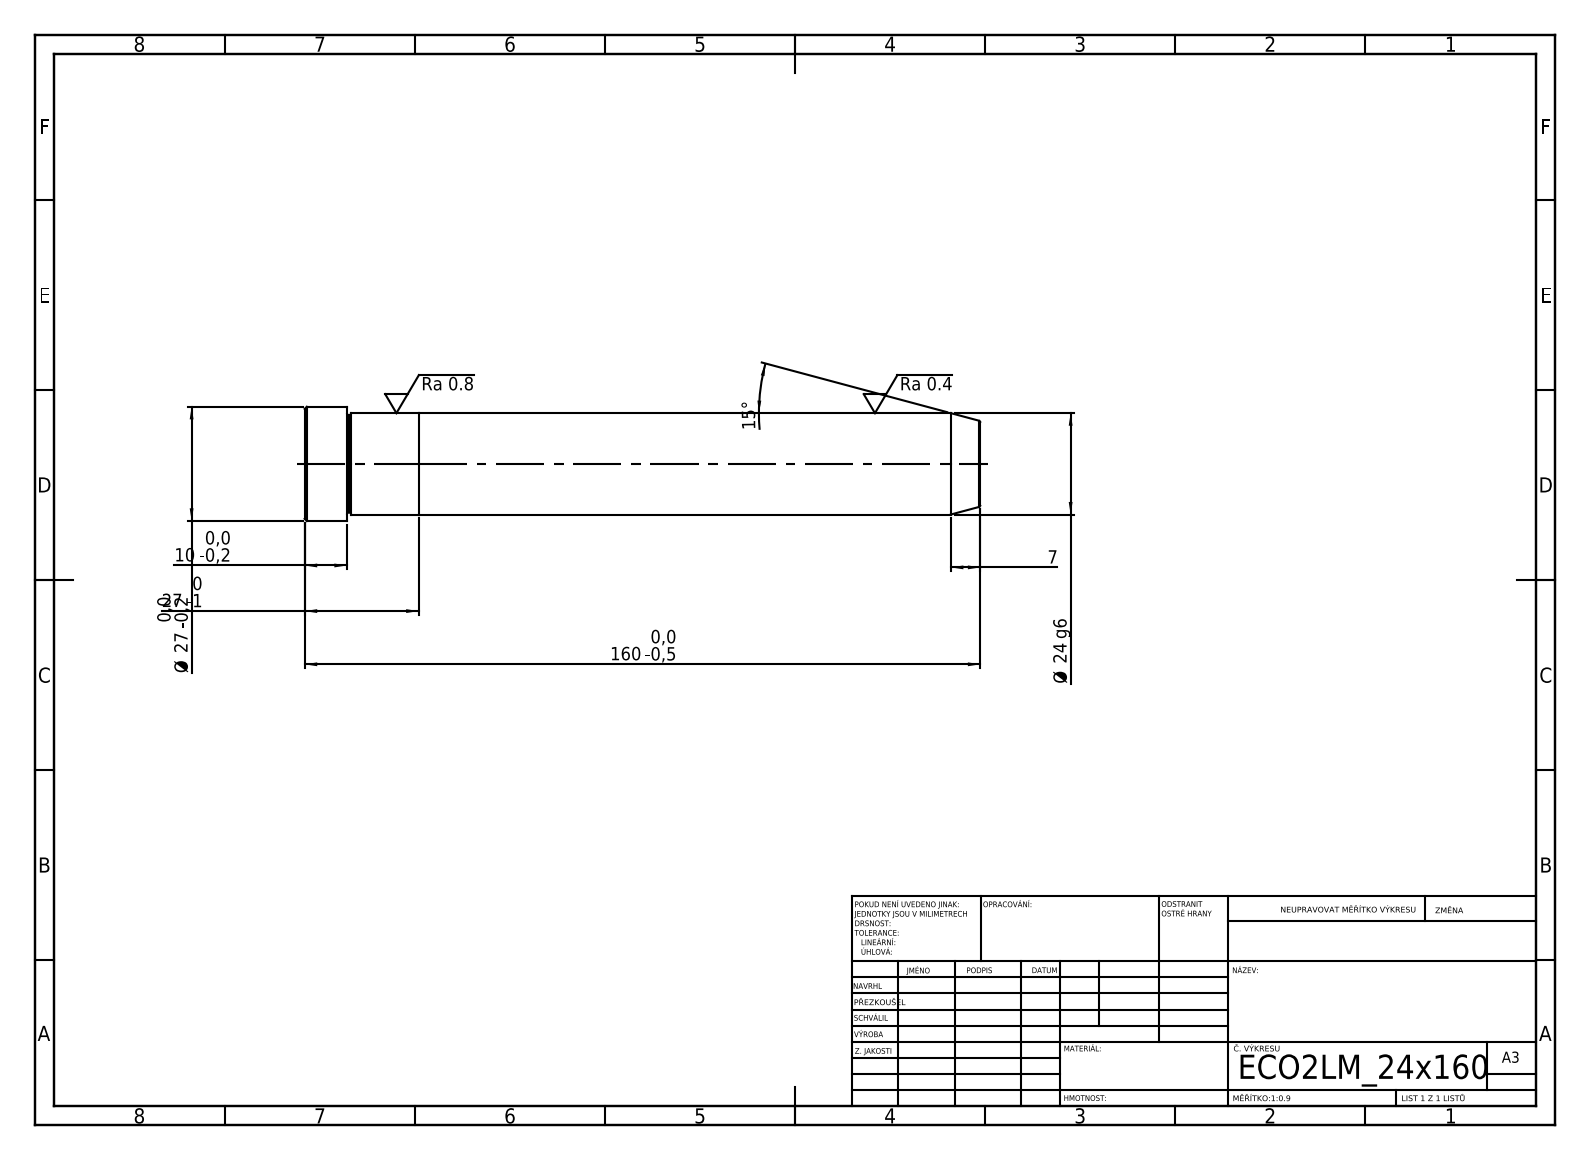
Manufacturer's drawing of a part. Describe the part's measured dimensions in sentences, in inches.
Its 3-D file was written by "SolidWorks 2019 (CONFIG_CONTROL_DESIGN)". It is 2 solids with 21 faces: 5 planar, 6 cylindrical and 10 other. Overall it measures 6.299 by 1.063 by 1.063 inches. Its volume is 4.459 cubic inches and its surface area 21.79 square inches. Round bosses or shafts: 1 of diameter 1.063, 1 of diameter 0.945. The main face-to-face distances are 1.063, 5.236, 6.299, 5.906, 0.669, 0.394.
